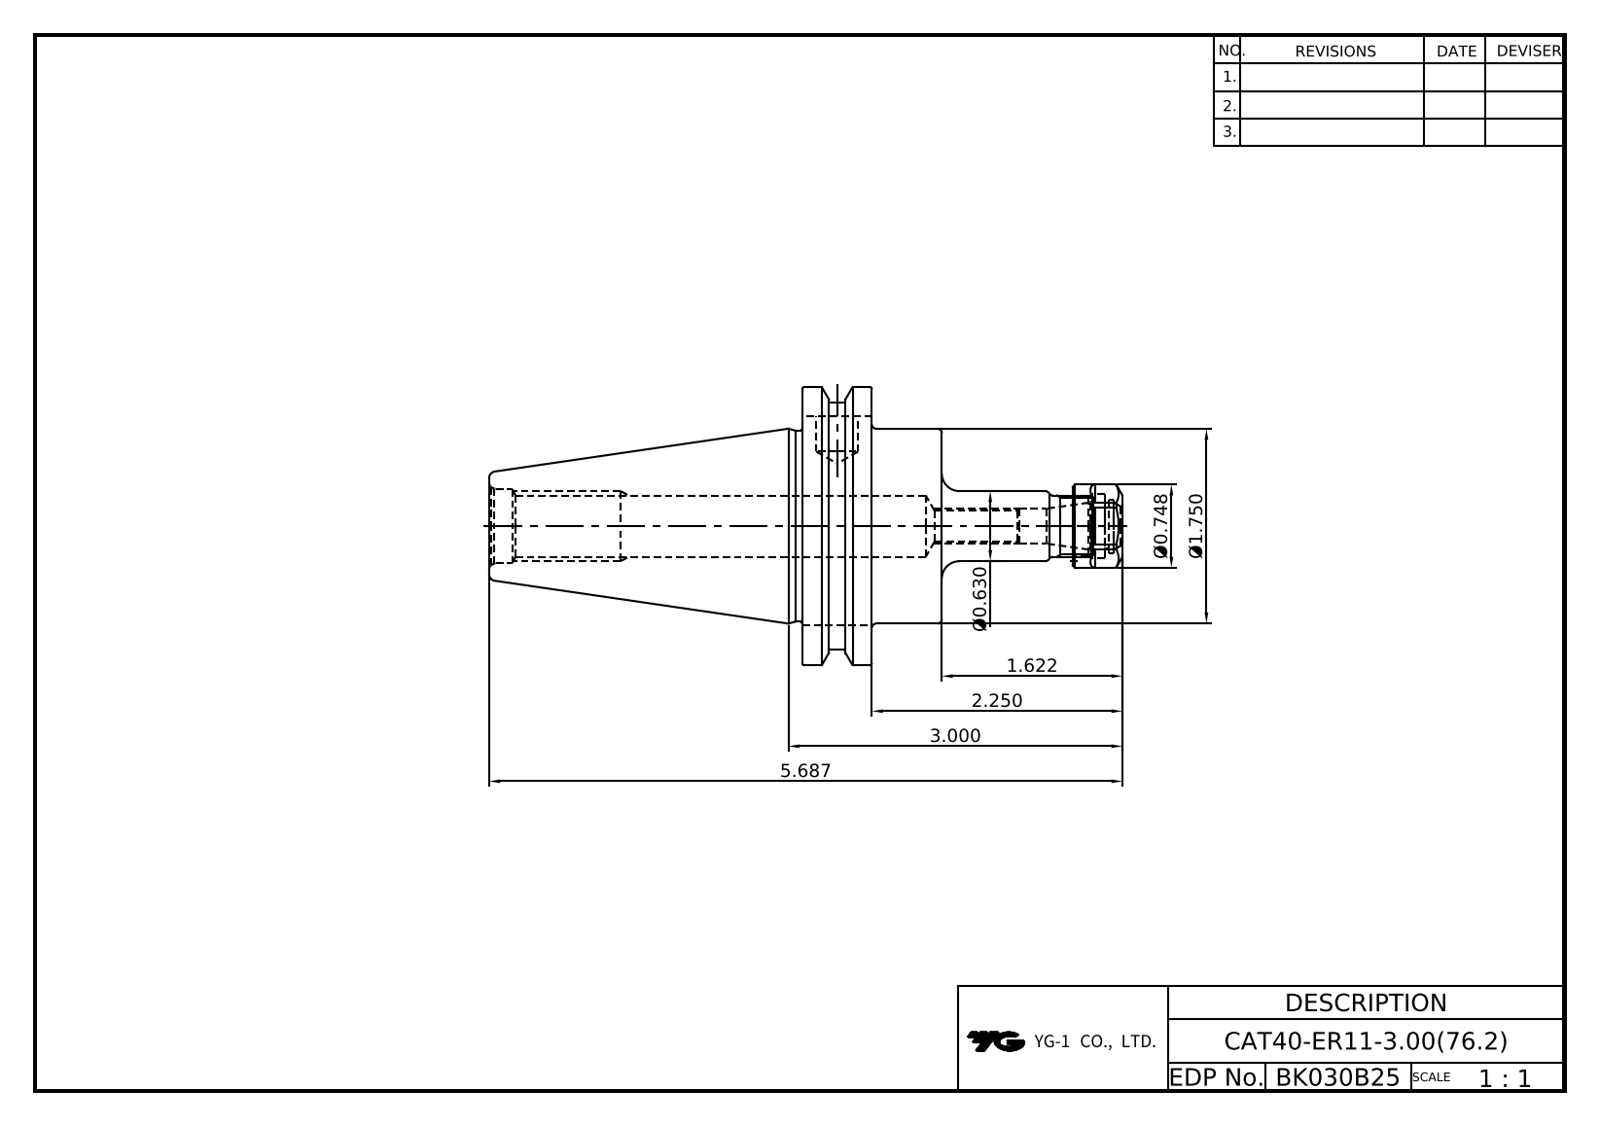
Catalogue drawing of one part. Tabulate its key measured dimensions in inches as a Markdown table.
| quantity | value |
| --- | --- |
| part name | LO-CAT40-ER11-76.2; ER11NUT |
| STEP written by | Autodesk Inventor 2025 (AUTOMOTIVE_DESIGN) |
| units | inches |
| bodies | 2 solids, 81 faces (45 planar, 18 cylindrical, 18 other) |
| overall size | 5.687 × 2.5 × 2.405 |
| volume | 7.942 in³ |
| surface area | 41.88 in² |
| round holes (diameter × count) | 0.252 × 1, 0.315 × 1, 0.339 × 1, 0.375 × 1, 0.527 × 1, 0.551 × 1, 0.642 × 1 |
| round bosses / shafts (diameter × count) | 2.5 × 1, 2.217 × 1, 1.75 × 1, 1.717 × 1, 0.748 × 1, 0.63 × 1 |
| main face-to-face distances | 0.628, 0.625, 1.253, 0.669, 1.874, 0.645, 2.812, 3.437, 4.065, 5.687 |
